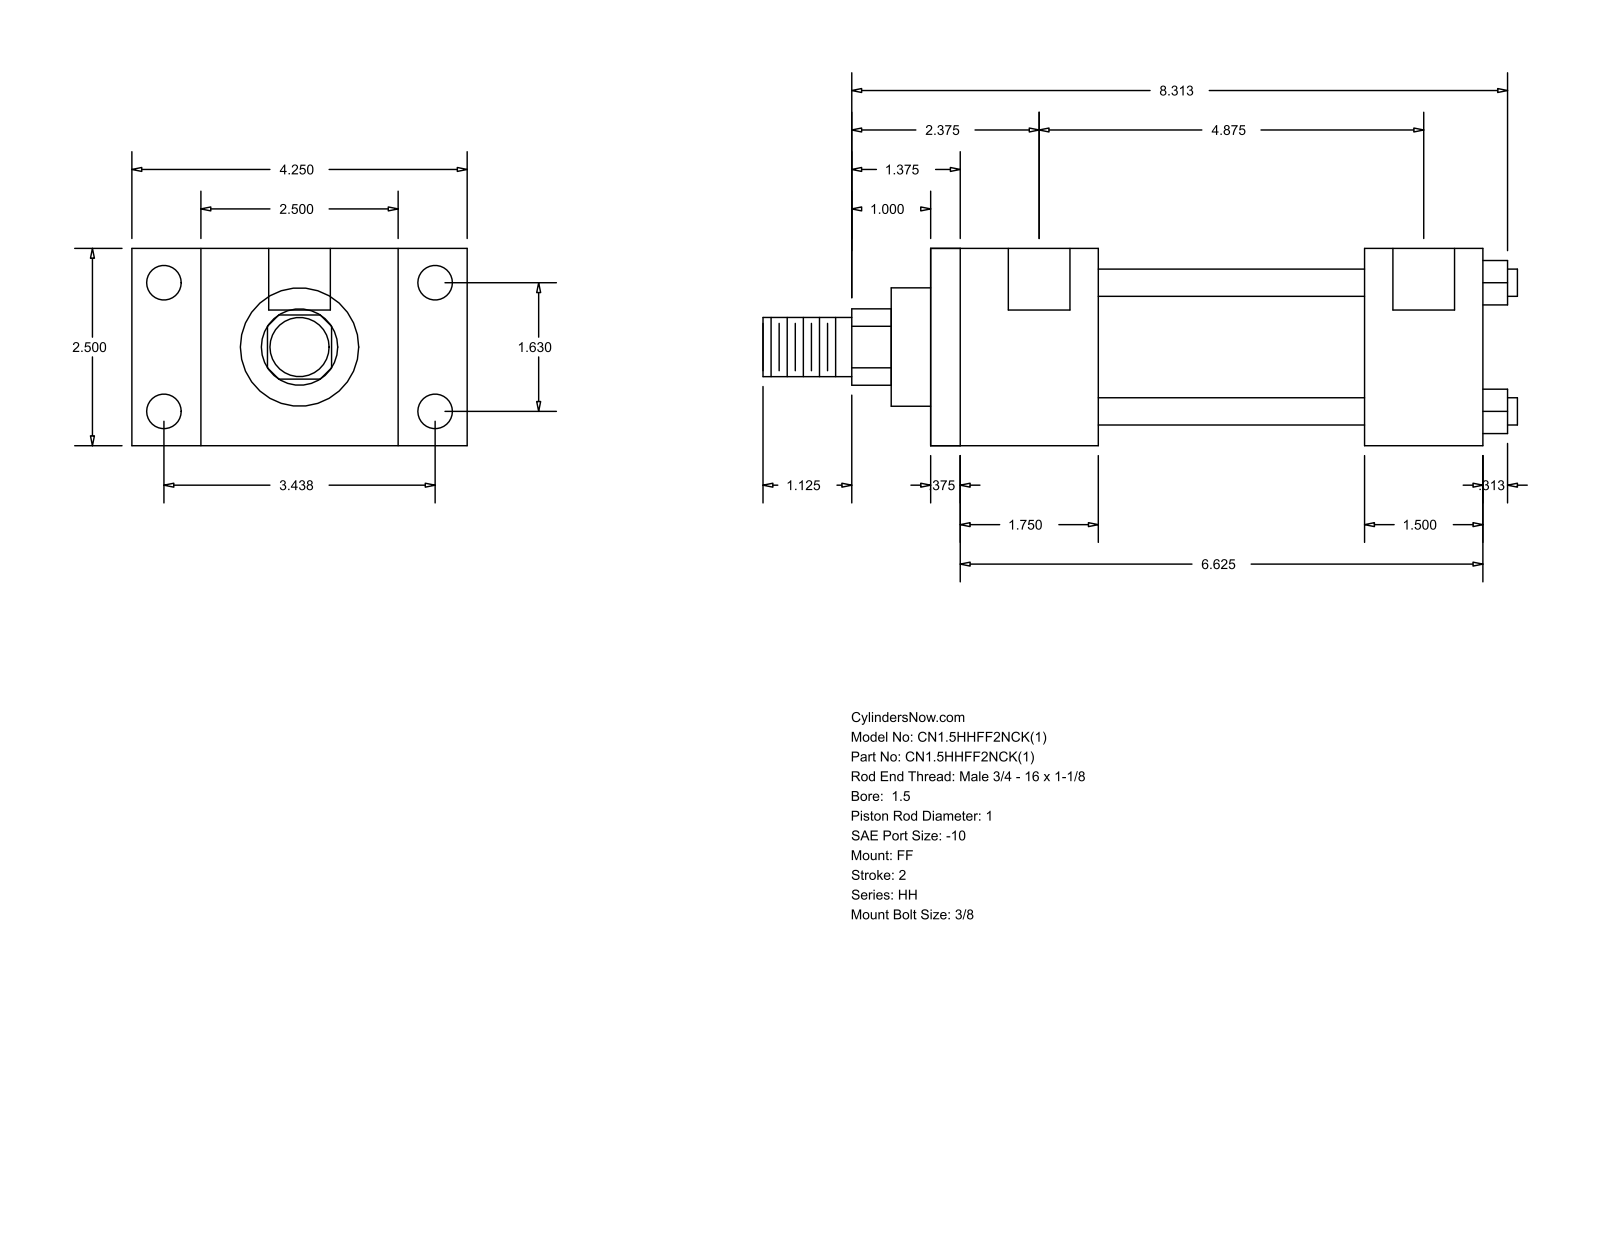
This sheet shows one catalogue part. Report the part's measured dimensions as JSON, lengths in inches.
{"part_name": "HH_FF__0150_1", "step_written_by": "GSSL Pune (CONFIG_CONTROL_DESIGN)", "units": "inches", "bodies": {"solids": 0, "faces": 92, "planar": 64, "cylindrical": 28, "other": 0}, "overall_size": [9.563, 4.25, 2.5], "round_holes": [[0.219, 4], [0.438, 4], [0.781, 2]], "round_bosses_or_shafts": [[0.345, 4], [1.75, 1], [1.5, 1], [1, 1], [0.75, 1]], "partial_cylinders_radius": [[0.484, 1]], "face_to_face_distances": [2.5, 7, 0.375, 6.625, 1.5, 2.125, 1.75, 4.875, 5.5, 5.125], "hole_center_spacings": [0.063, 1.63, 3.438, 3.805, 4.937, 5, 4.875]}
